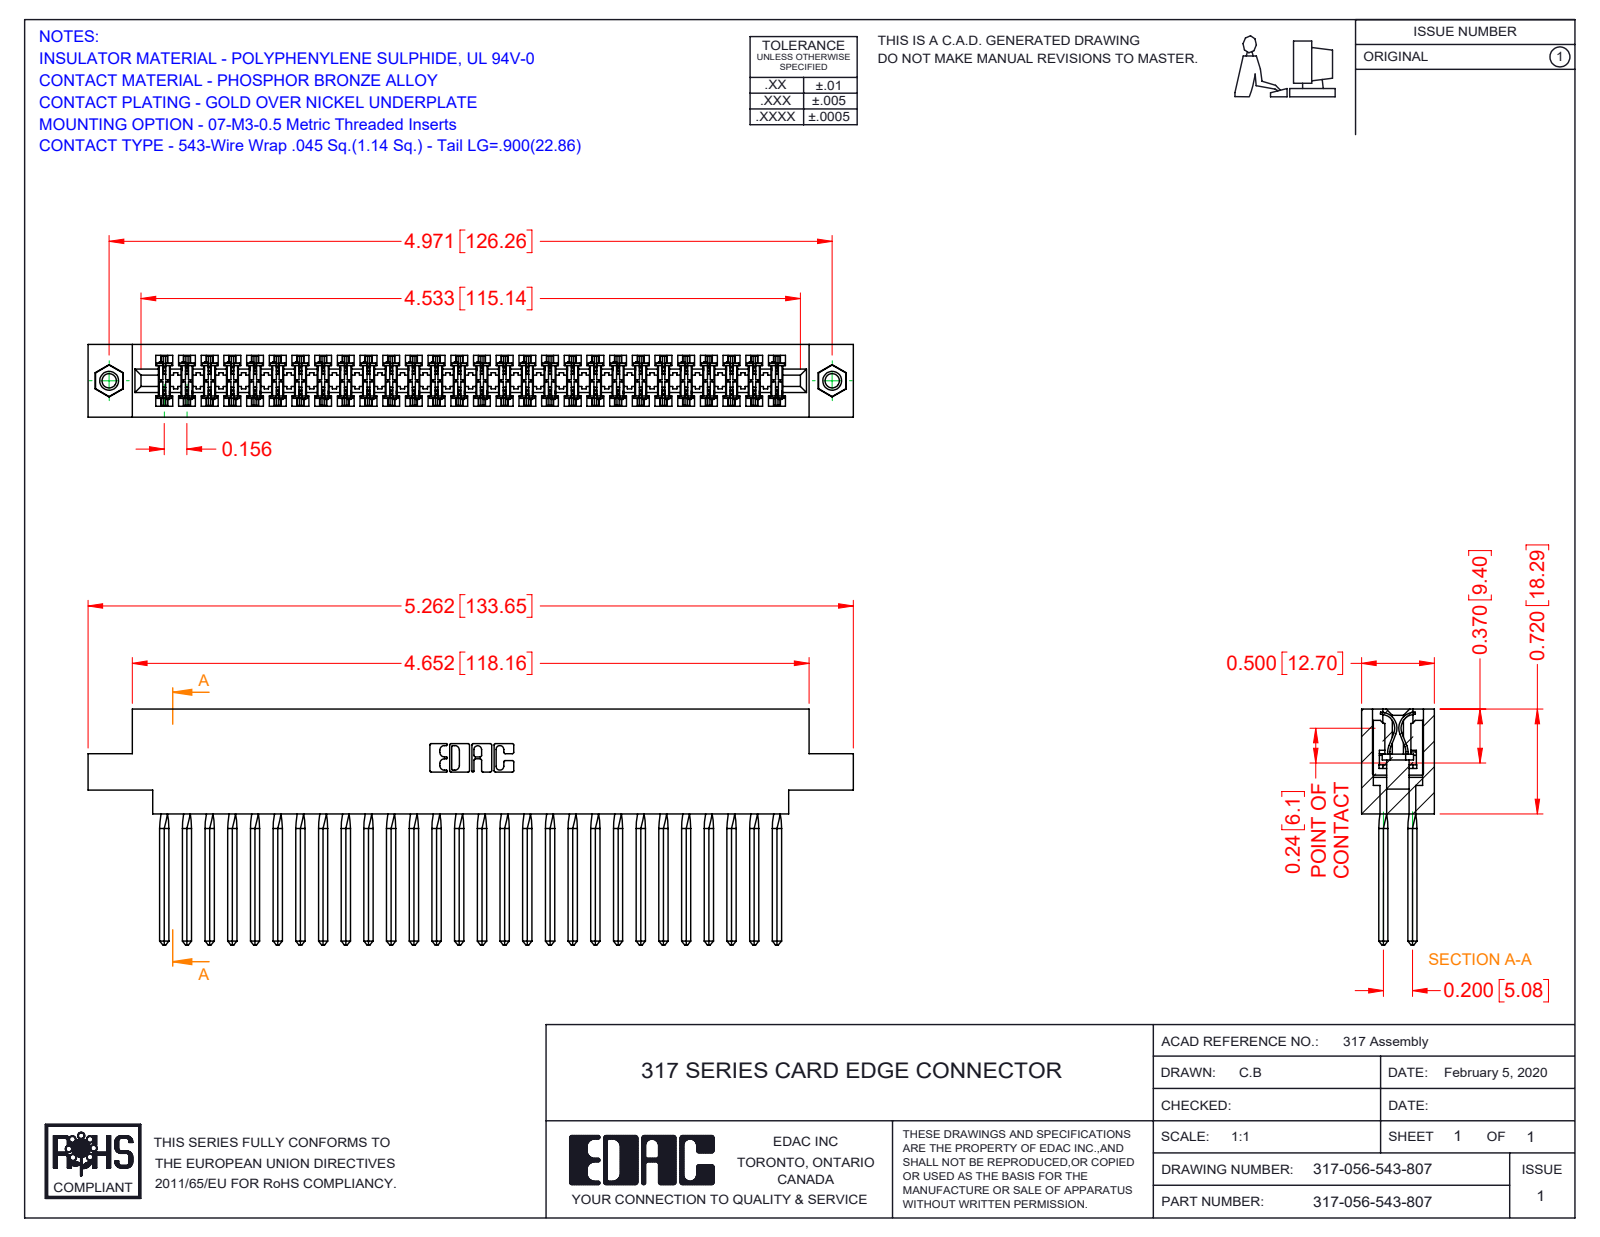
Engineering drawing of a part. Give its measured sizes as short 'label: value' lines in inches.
name: 345-250-001_345-250-005-103; 317 Part_.156 Dia - TI; 317-290-001_543; 317-056-543-807
written by: SolidWorks 2016 (CONFIG_CONTROL_DESIGN)
unit: in
bodies: 59 solids, 5146 faces (4178 planar, 728 cylindrical, 240 other)
size: 5.262 × 1.62 × 0.5
volume: 1.356 in³; area: 51.46 in²
holes: 2× ⌀0.098, 2× ⌀0.125, 2× ⌀0.156
bosses: 2× ⌀0.155
rounds: 112× R0.015, 22× R0.01, 6× R0.007, 6× R0.031, 3× R0.026, 2× R0.095, 2× R0.1, 2× R0.11
face distances: 0.5, 0.075, 0.425, 0.35, 0.11, 0.195, 0.094, 0.2, 0.72, 0.115
hole spacings: 4.971
